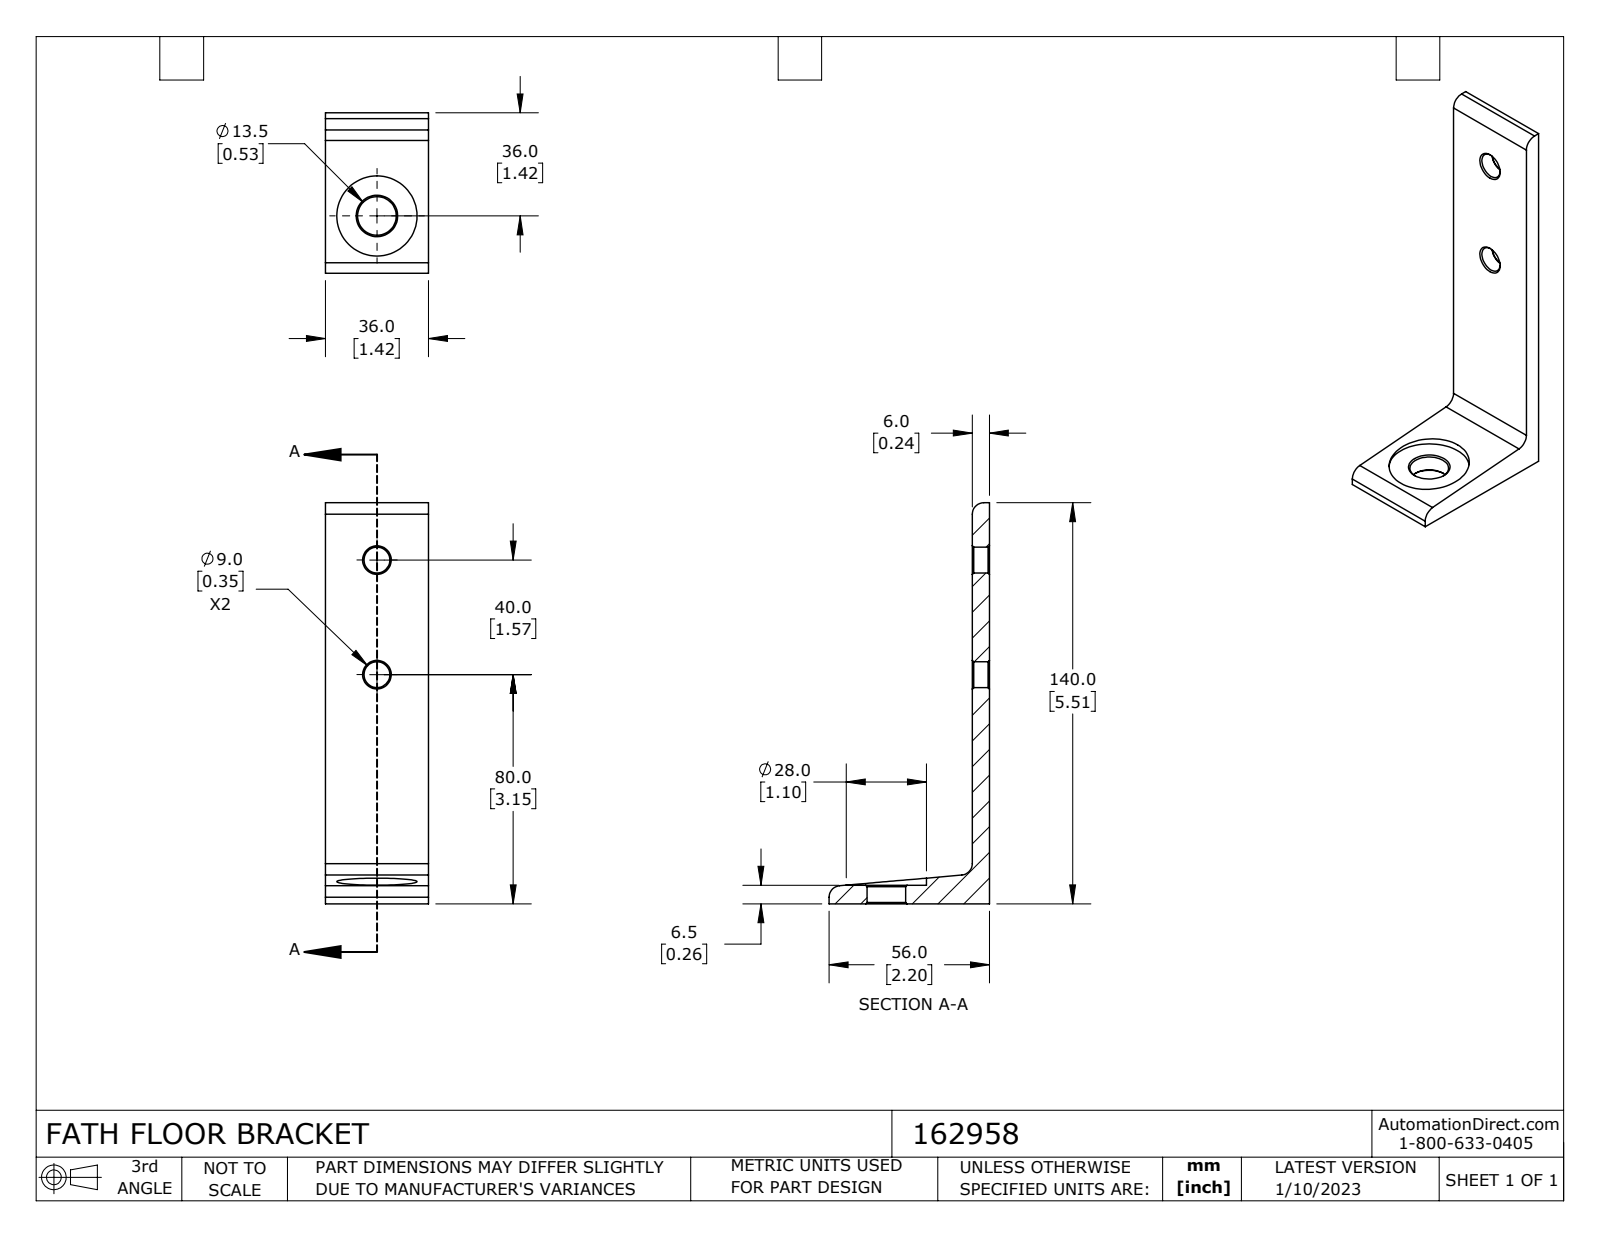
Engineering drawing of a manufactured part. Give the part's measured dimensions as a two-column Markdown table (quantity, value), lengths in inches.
| quantity | value |
| --- | --- |
| part name | 162958 |
| STEP written by | SolidWorks 2021 (CONFIG_CONTROL_DESIGN) |
| units | inches |
| bodies | 1 solid, 32 faces (9 planar, 11 cylindrical, 12 other) |
| overall size | 5.512 × 2.205 × 1.417 |
| volume | 2.585 in³ |
| surface area | 25.45 in² |
| round holes (diameter × count) | 0.354 × 2, 0.531 × 1, 1.102 × 1 |
| partial cylindrical surfaces (radius × count) | 0.157 × 3 |
| main face-to-face distances | 0.236, 1.417, 0.256, 2.205, 1.969, 5.512, 5.256 |
| hole center spacings | 1.575 |
